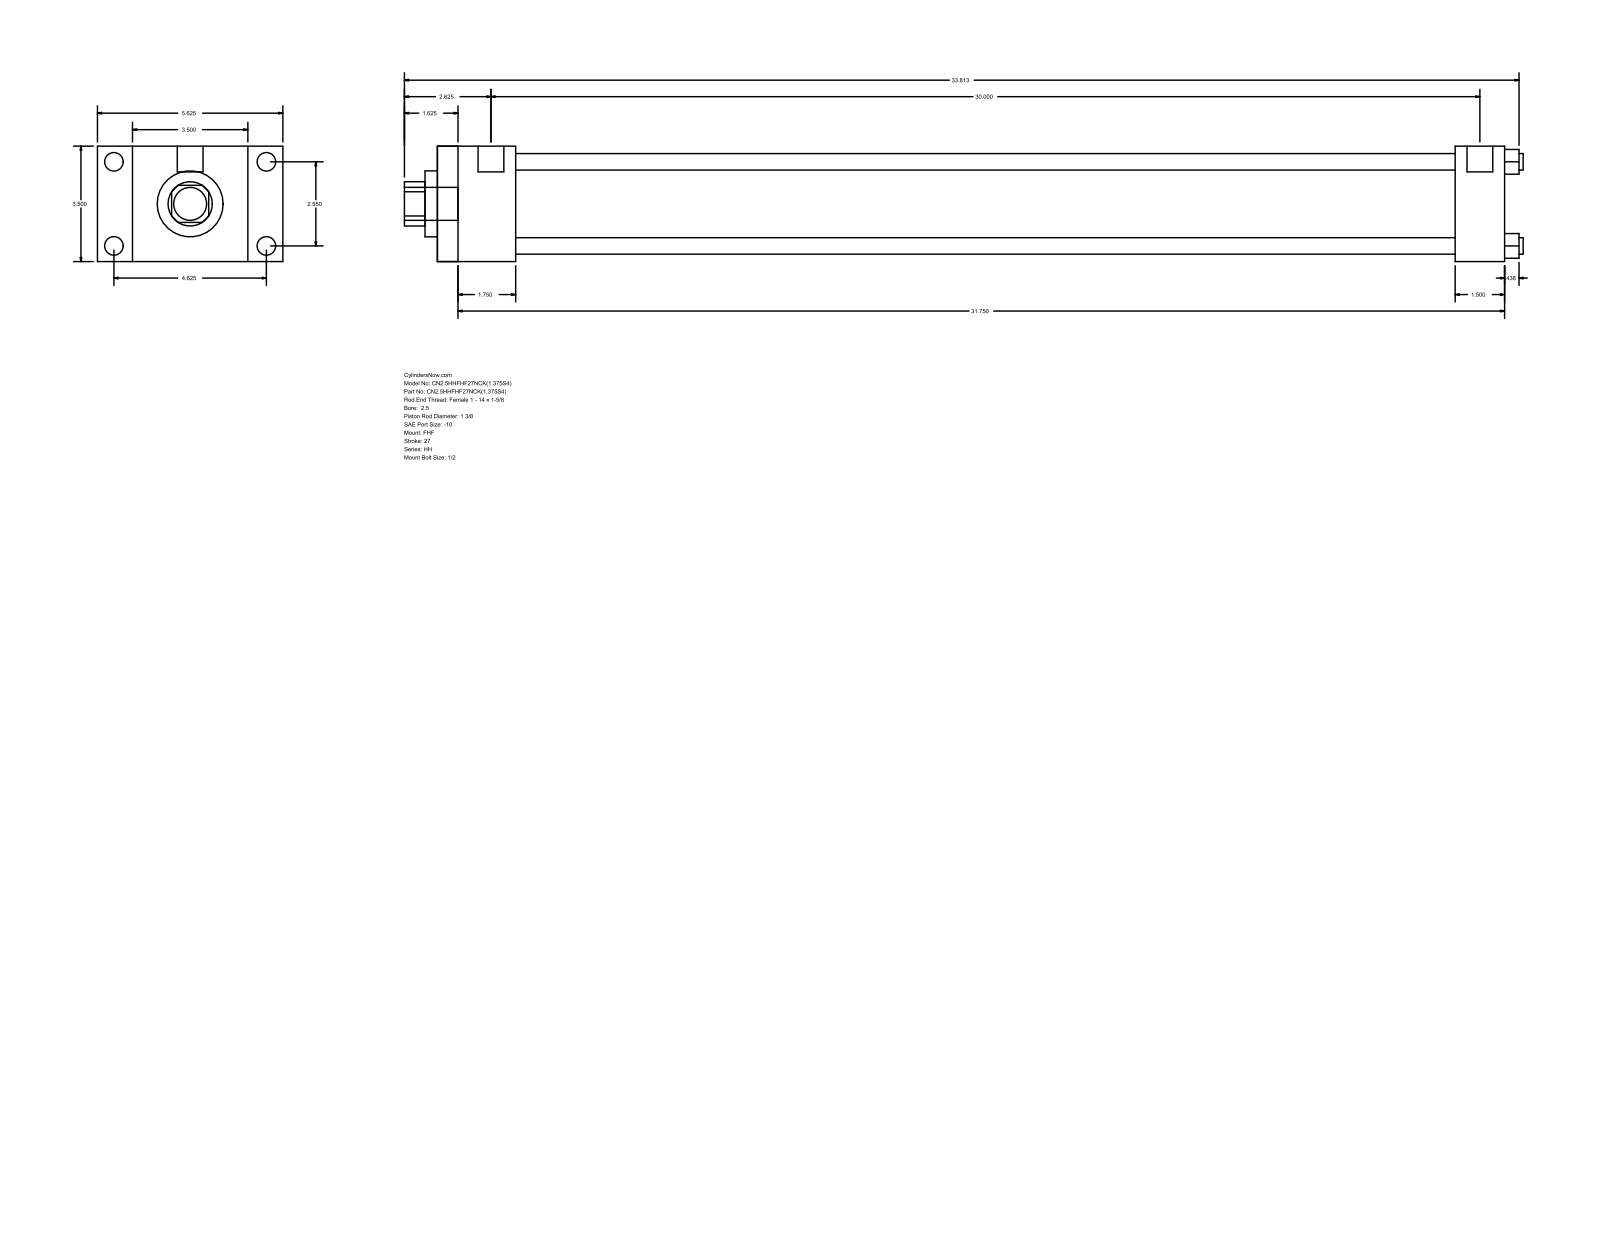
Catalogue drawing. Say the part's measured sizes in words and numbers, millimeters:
The part is named "HH_FHF__0250_1.375". Its 3-D file was written by "GSSL Pune (CONFIG_CONTROL_DESIGN)". It is 0 solids with 88 faces: 60 planar, 28 cylindrical and 0 other. Overall it measures 862.01 by 142.88 by 88.9 millimeters. Round holes: 4 of diameter 12.7, 1 of diameter 34.92, 1 of diameter 50.8, 1 of diameter 73.03. Round bosses or shafts: 4 of diameter 14.3, 4 of diameter 5.56, 2 of diameter 19.84, 1 of diameter 25.4. Partial cylindrical surfaces (rounded edges, fillets, slot ends): 1 of radius 17.06. The main face-to-face distances are 88.9, 60.32, 26.99, 115.89, 822.33, 762.01, 142.88, 784.22, 723.9, 38.11. The hole center spacings are 45.79, 64.76, 91.58.
